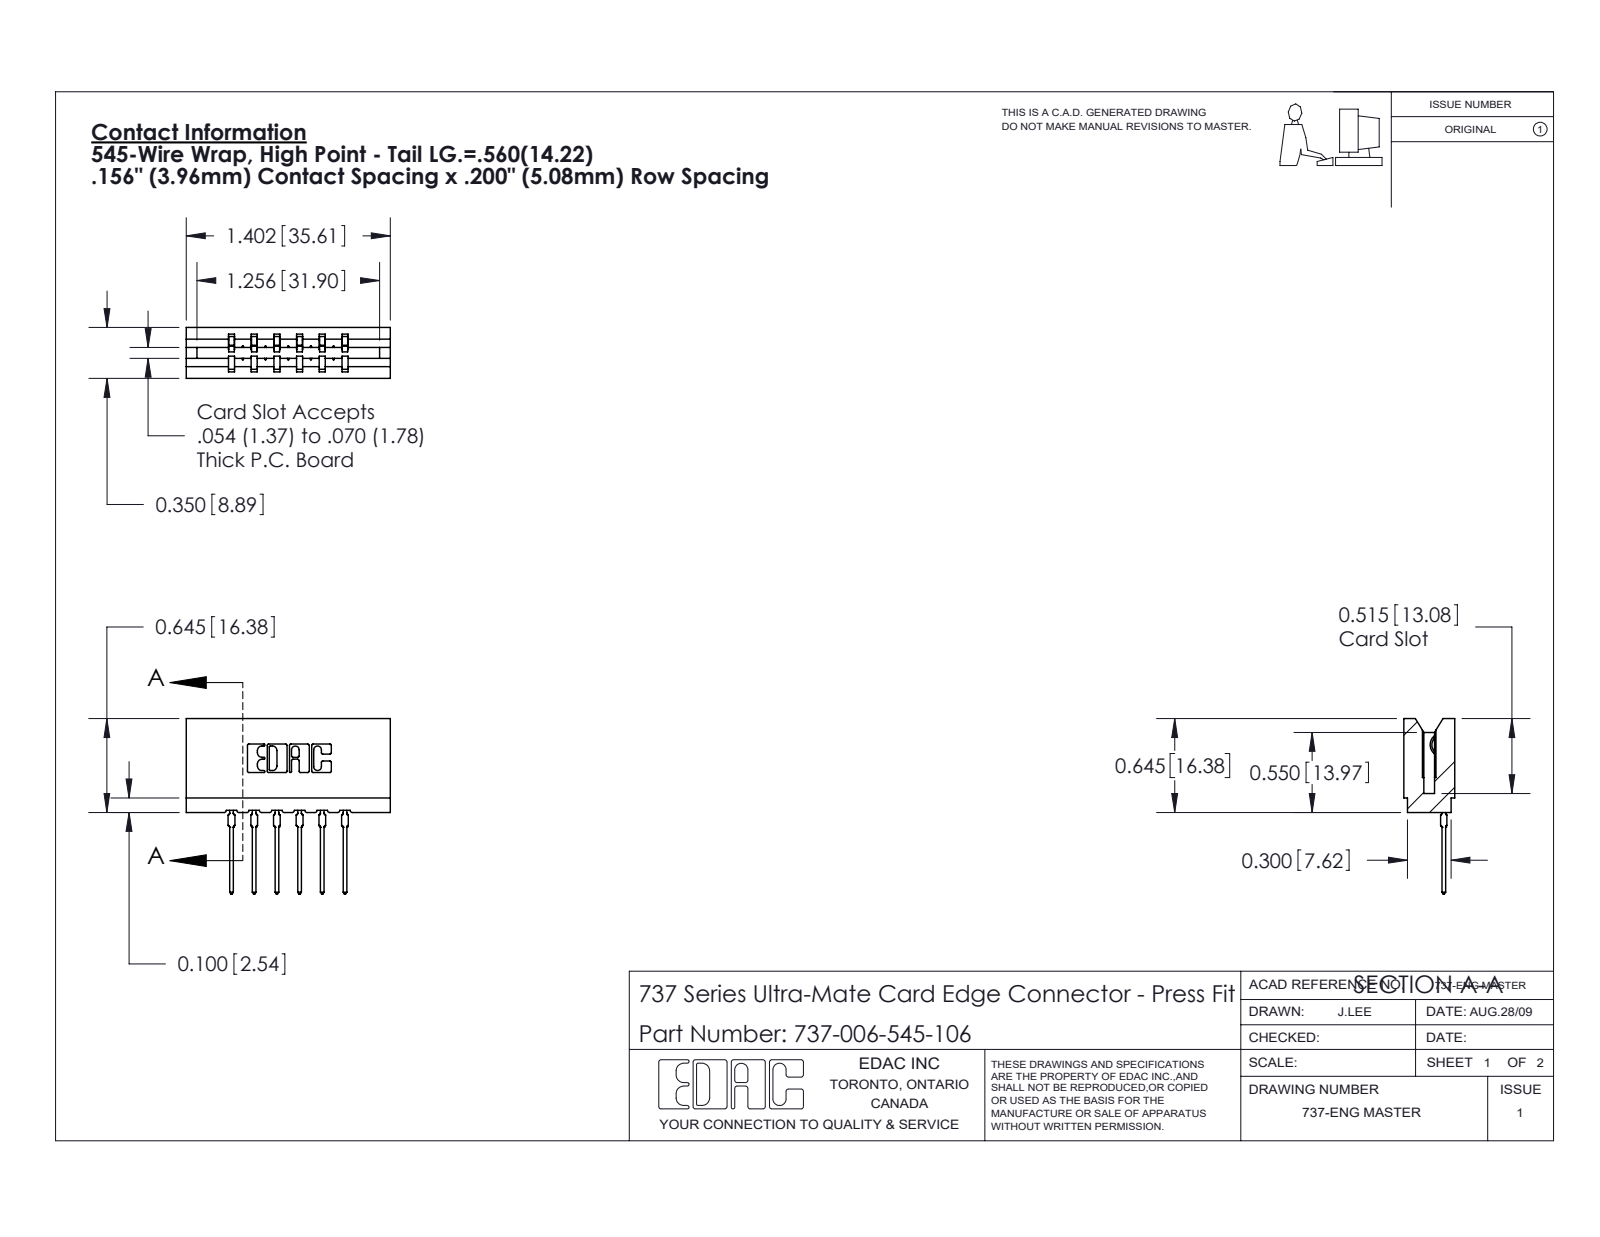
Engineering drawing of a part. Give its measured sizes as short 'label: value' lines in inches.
name: 737 Part_Insulator Option - 06; 745-292-001_545; 737-006-545-106
written by: SolidWorks 2020 (CONFIG_CONTROL_DESIGN)
unit: in
bodies: 7 solids, 773 faces (463 planar, 154 cylindrical, 156 other)
size: 1.402 × 1.206 × 0.35
volume: 0.225 in³; area: 6.813 in²
rounds: 22× R0.01, 12× R0.015, 12× R0.021, 6× R0.007, 6× R0.031, 4× R0.005, 4× R0.011, 3× R0.026
face distances: 0.156, 0.138, 0.212, 0.35, 0.312, 0.354, 0.198, 0.074, 0.468, 0.51
